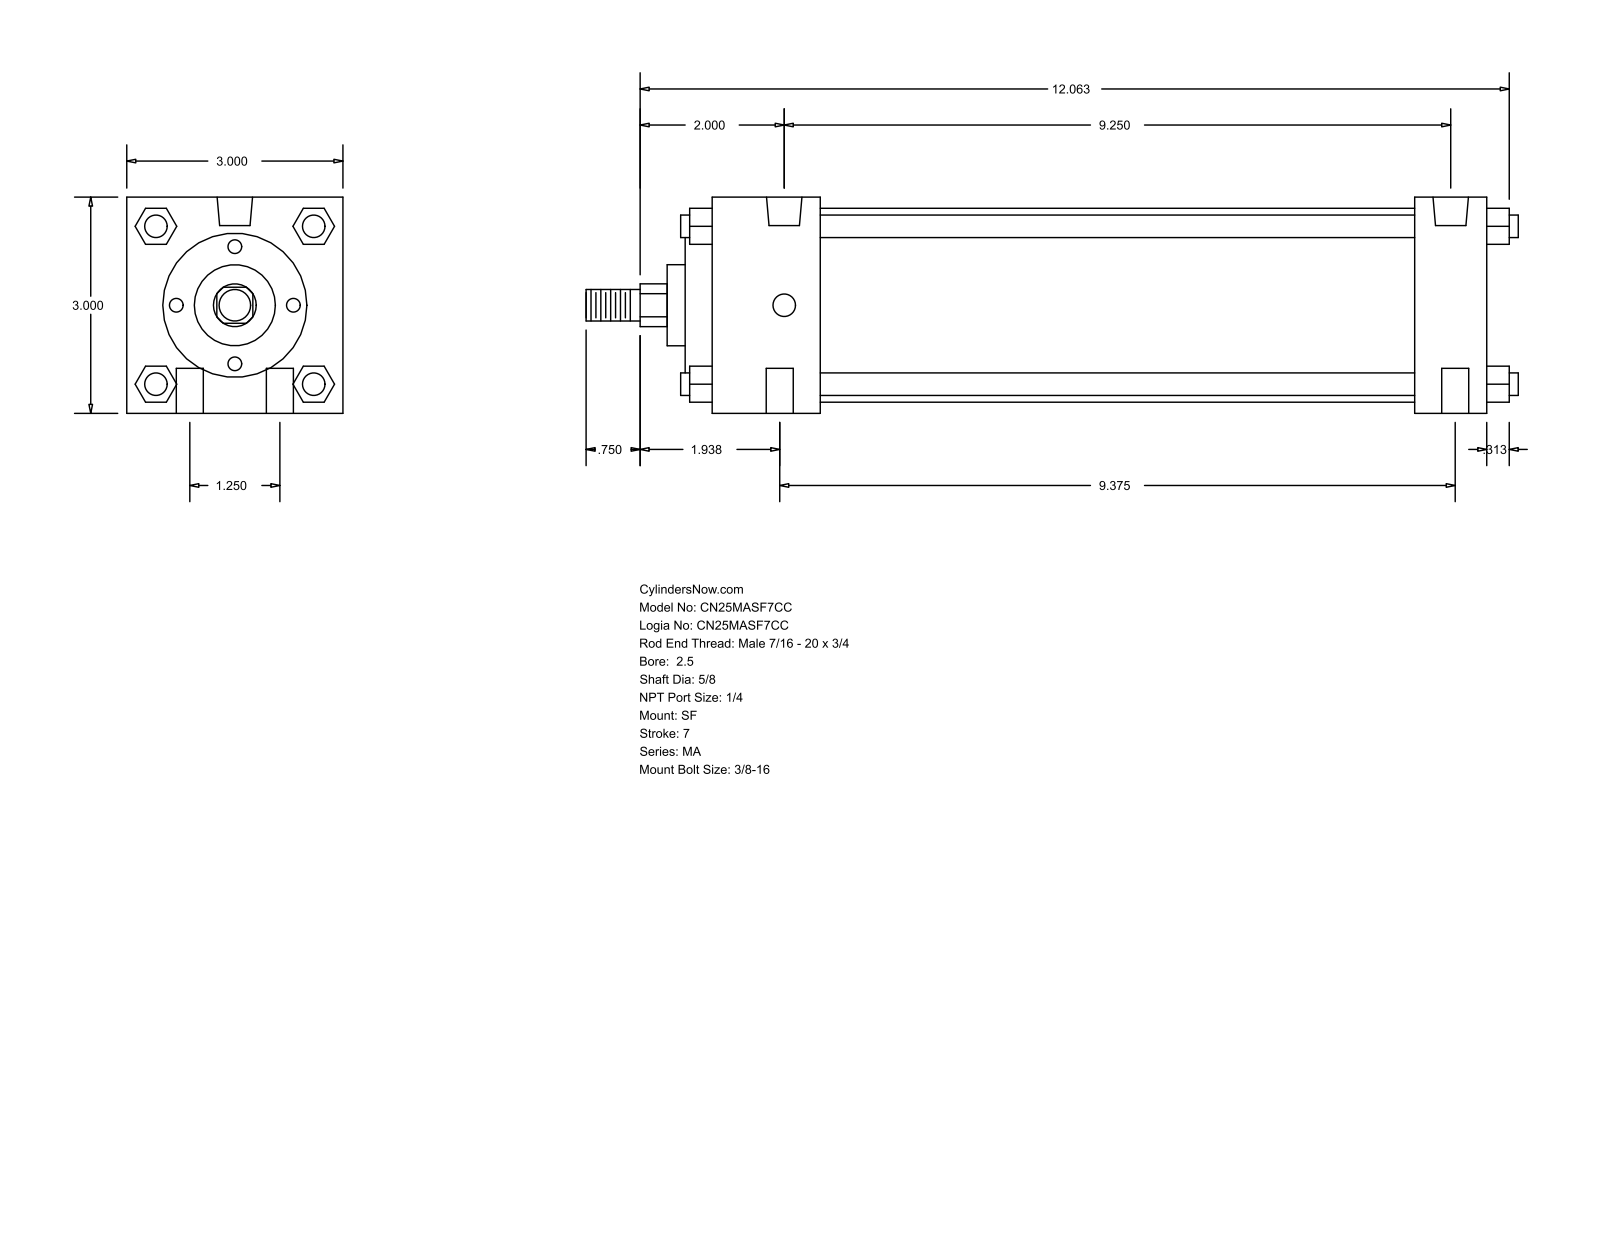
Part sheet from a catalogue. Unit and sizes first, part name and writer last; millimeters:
Units: millimetres
Overall size (bounding box): 328.61 × 76.2 × 76.2
Round holes (diameter × count): ⌀9.53 ×4, ⌀7.94 ×2, ⌀12.49 ×2
Round bosses / shafts (diameter × count): ⌀7.94 ×4, ⌀68.33 ×1, ⌀50.8 ×1, ⌀28.57 ×1, ⌀15.88 ×1, ⌀11.11 ×1
Partial cylindrical surfaces — rounded edges, fillets, slot ends (radius × count): R7.54 ×1
Main face-to-face distances: 76.2, 273.05, 25.4, 247.65, 38.1, 209.55, 234.95, 12.7, 9.52, 47.62
Hole centre spacings: 15.96, 237.07, 31.76, 234.95, 238.13, 240.24
Bodies: 0 solids, 126 faces (95 planar, 31 cylindrical, 0 other)
Part name (STEP PRODUCT): MA_SF__0250_0.625
STEP written by: GSSL Pune (CONFIG_CONTROL_DESIGN)
